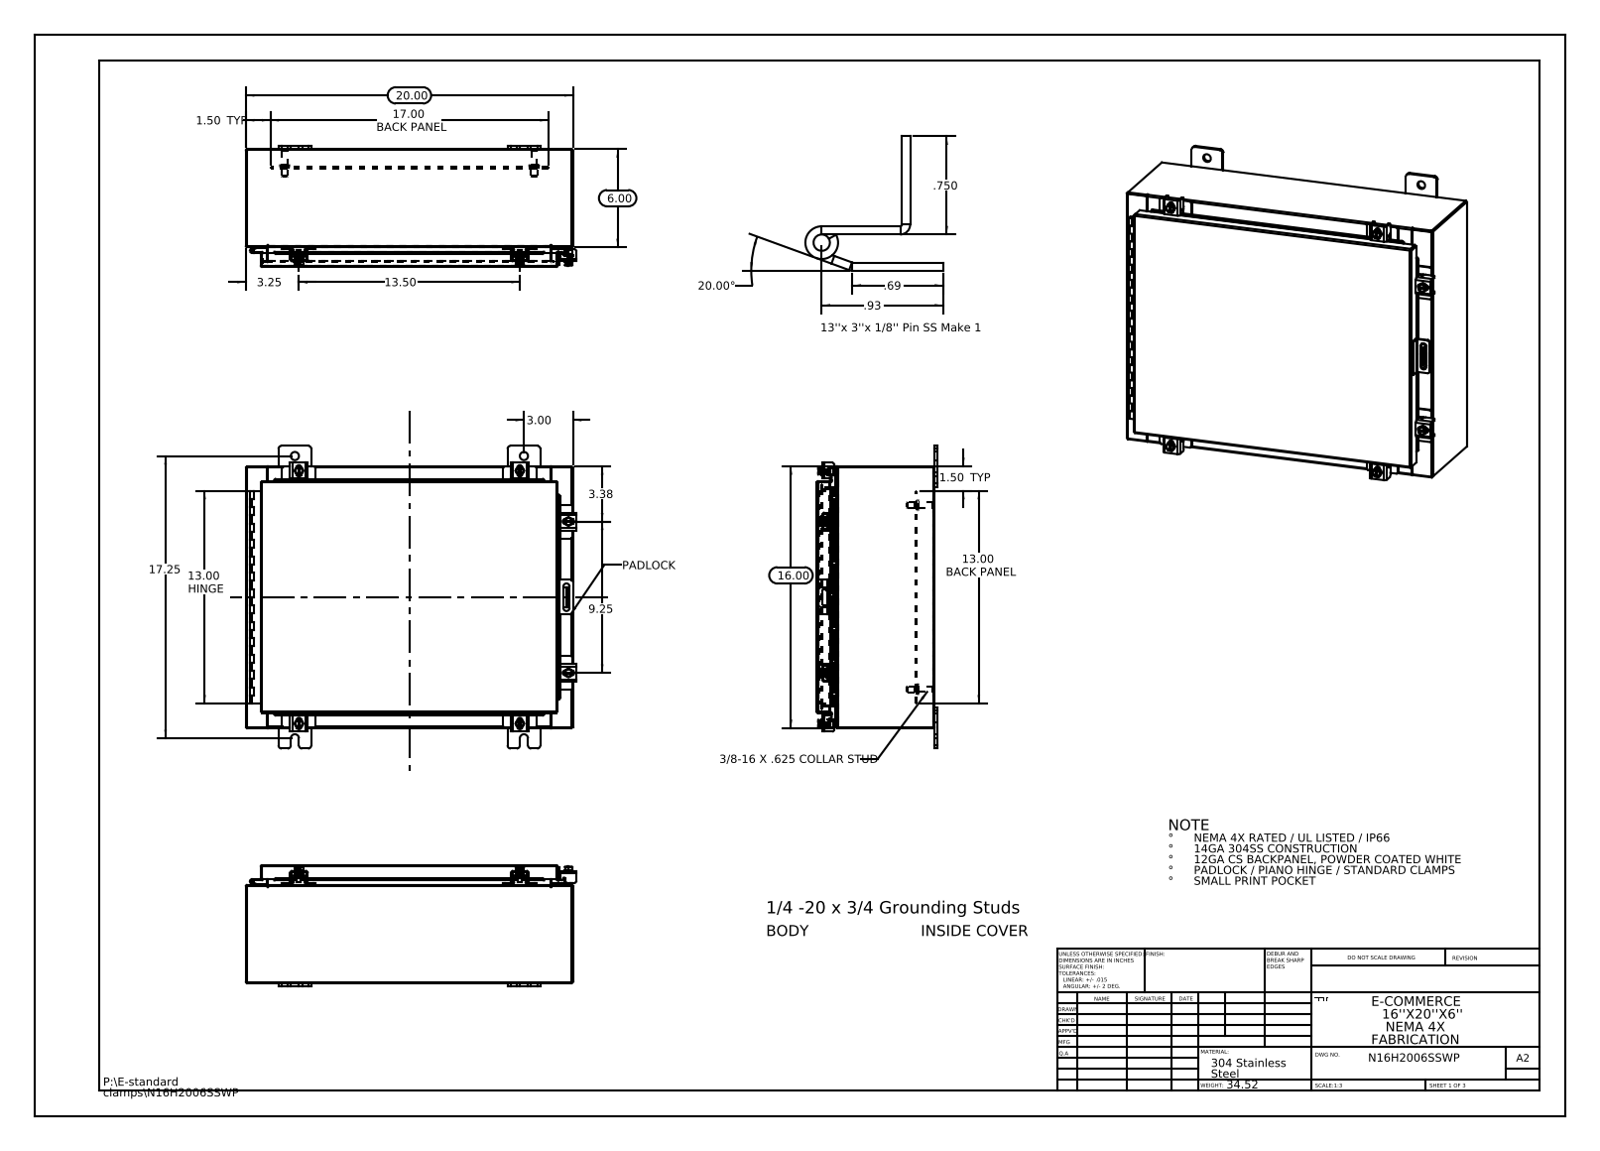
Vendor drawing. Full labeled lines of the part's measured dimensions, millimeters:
Part name (STEP PRODUCT): N16H2006SSWP Hinge Cover Side; N16H2006SSWP Body; N16H2006SSWP 22104005_DEFAULT; N16H2006SSWP Bottom (+8 more)
STEP written by: SolidWorks 2013 (CONFIG_CONTROL_DESIGN)
Units: millimetres
Bodies: 47 solids, 1501 faces (800 planar, 605 cylindrical, 96 other)
Overall size (bounding box): 513.4 × 469.9 × 187.7
Volume: 2 001 000 mm³ · Surface area: 1 991 000 mm²
Round holes (diameter × count): ⌀12.7 ×8, ⌀5.4 ×6, ⌀6.6 ×6, ⌀3.2 ×2, ⌀3.2 ×1
Round bosses / shafts (diameter × count): ⌀6.4 ×7, ⌀12.7 ×6, ⌀10.1 ×6, ⌀15.9 ×4, ⌀9.5 ×4, ⌀8.4 ×4
Partial cylindrical surfaces — rounded edges, fillets, slot ends (radius × count): R1.5 ×30, R4.8 ×24, R0.3 ×23, R2.2 ×21, R3 ×12, R3.6 ×12, R3.2 ×10, R1.3 ×9
Main face-to-face distances: 1.9, 181, 182.9, 179.1, 404.5, 25.4, 27.3, 153.7, 155.6, 29.9
Hole centre spacings: 339.9, 498.3, 10.9, 23.7, 47.2, 57.8, 57.8, 59.1
